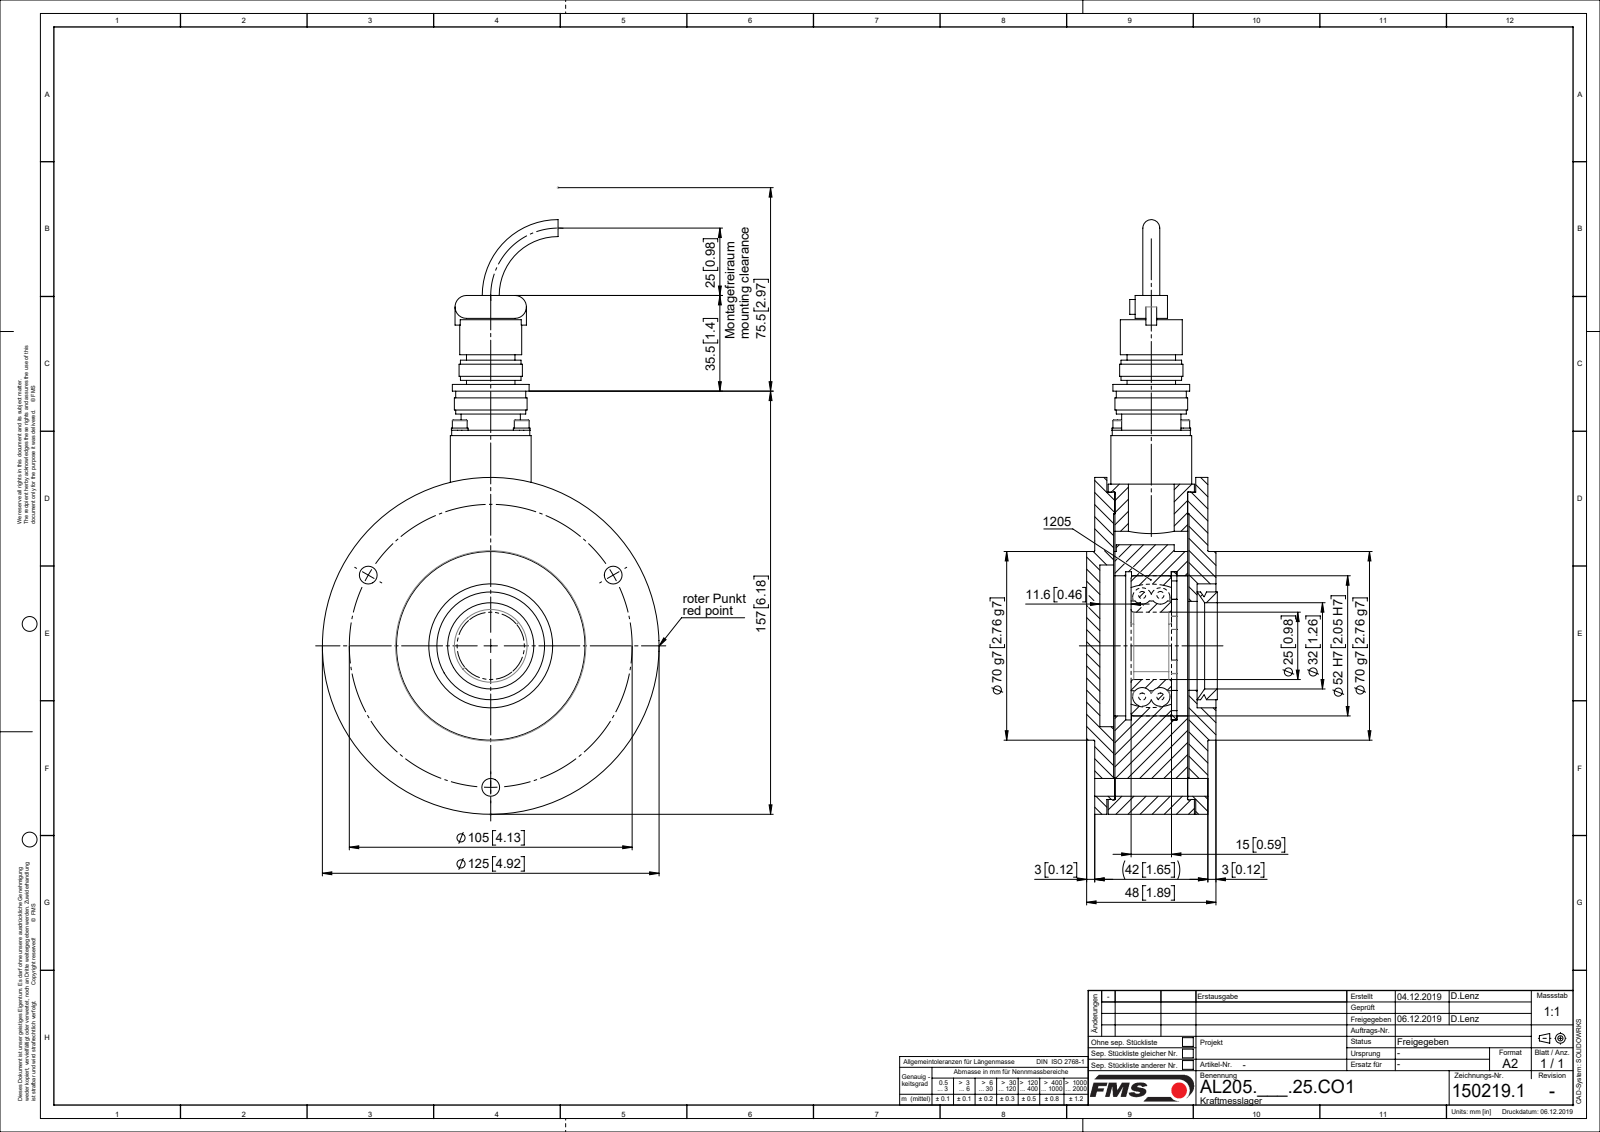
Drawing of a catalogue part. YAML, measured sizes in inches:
part_name: "Federringe_DIN127A_M03; 130124.5_stp_01; 150219.1_stp; Zyl-Schr DIN912_M3x25 (+7 more)"
step_written_by: "SolidWorks 2018 (CONFIG_CONTROL_DESIGN)"
units: inches
bodies: {solids: 41, faces: 451, planar: 124, cylindrical: 207, other: 120}
overall_size: [8.687, 4.921, 1.909]
volume: 29.3
surface_area: 212.3
round_holes:
  - {diameter: 0.26, count: 10}
  - {diameter: 0.098, count: 6}
  - {diameter: 0.122, count: 4}
  - {diameter: 0.134, count: 4}
  - {diameter: 0.157, count: 1}
  - {diameter: 0.669, count: 1}
  - {diameter: 0.906, count: 1}
  - {diameter: 0.984, count: 1}
  - {diameter: 1.26, count: 1}
  - {diameter: 1.299, count: 1}
  - {diameter: 1.811, count: 1}
  - {diameter: 2.047, count: 1}
round_bosses_or_shafts:
  - {diameter: 0.217, count: 6}
  - {diameter: 0.244, count: 4}
  - {diameter: 0.118, count: 4}
  - {diameter: 0.098, count: 4}
  - {diameter: 4.921, count: 1}
  - {diameter: 2.756, count: 1}
  - {diameter: 1.575, count: 1}
  - {diameter: 1.311, count: 1}
partial_cylinders:
  - {radius: 0.004, count: 4}
  - {radius: 0.167, count: 2}
  - {radius: 0.167, count: 2}
  - {radius: 0.819, count: 1}
  - {radius: 0.949, count: 1}
face_to_face_distances: [0.295, 0.02, 1.358, 0.276, 1.378, 1.083, 0.118, 1.476, 1.063, 1.181]
hole_center_spacings: [2.067, 0.55, 0.64, 0.906, 1.518, 1.87, 2.402, 2.645]
